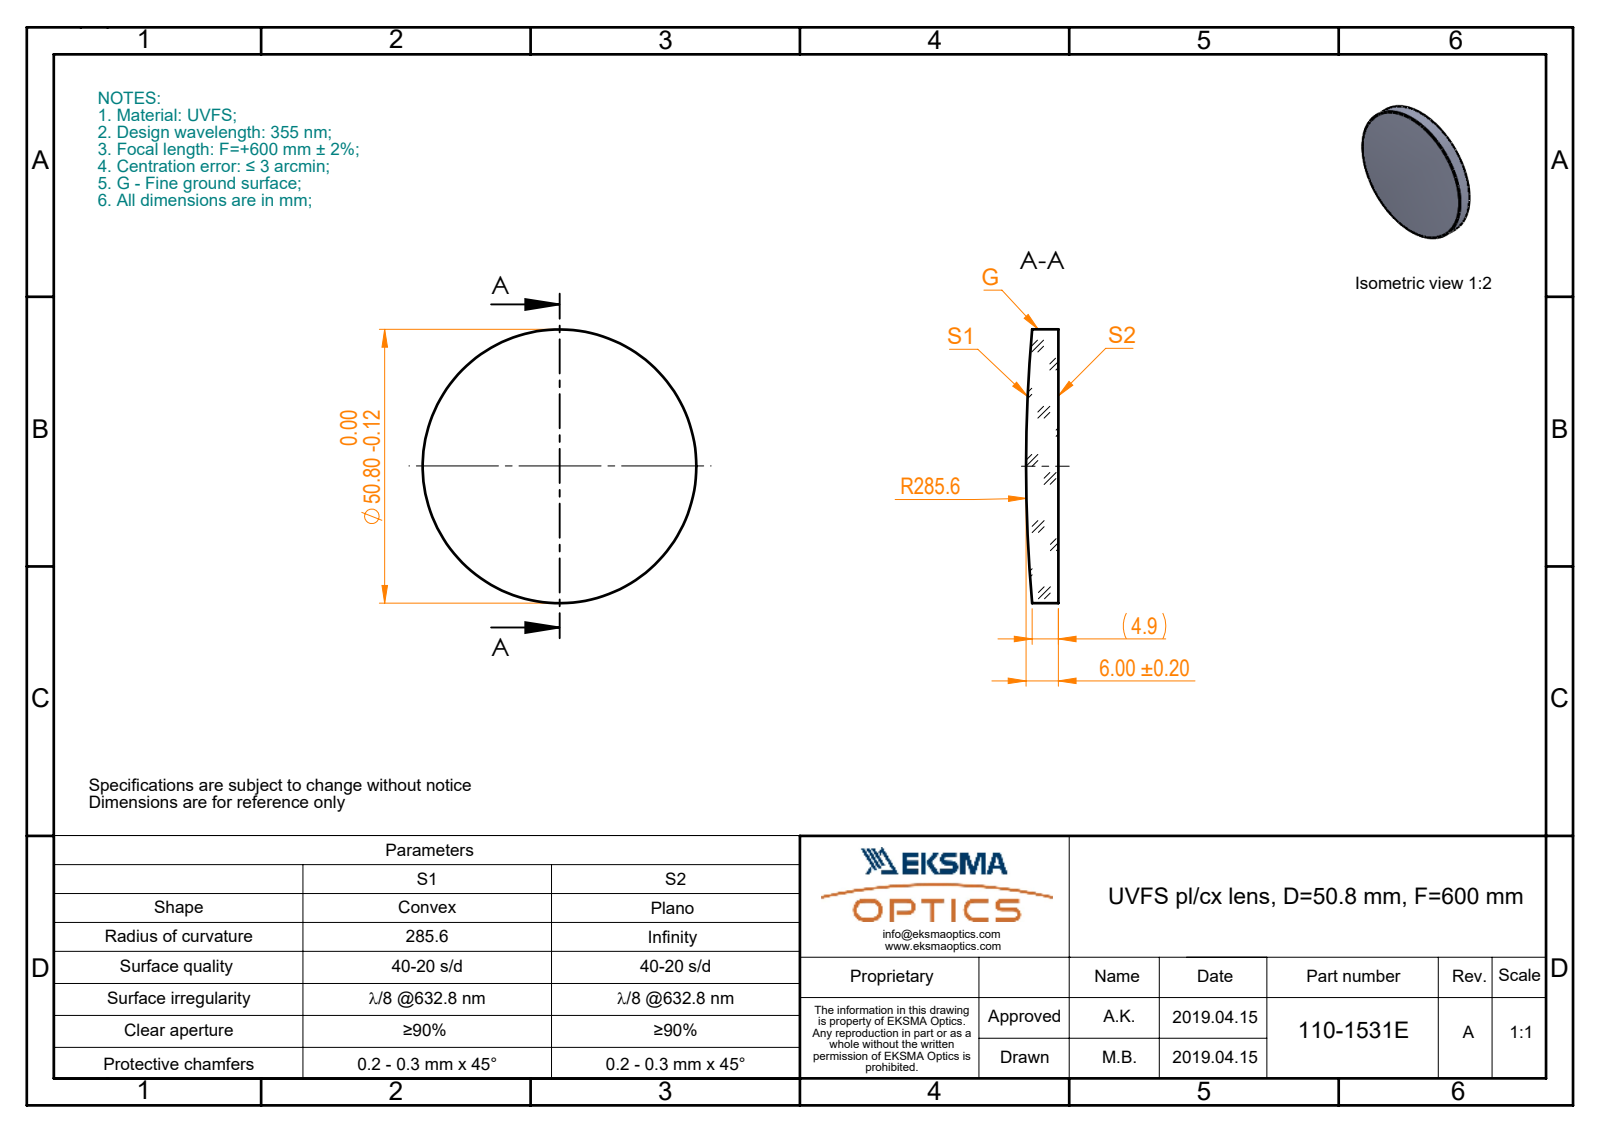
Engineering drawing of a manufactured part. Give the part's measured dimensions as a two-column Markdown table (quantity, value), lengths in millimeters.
| quantity | value |
| --- | --- |
| part name | 110-1531E UVFS pl-cx 50.8 F600 |
| STEP written by | SolidWorks 2017 (CONFIG_CONTROL_DESIGN) |
| units | millimeters |
| bodies | 1 solid, 5 faces (1 planar, 2 cylindrical, 2 other) |
| overall size | 50.8 × 50.8 × 6 |
| volume | 11 015 mm³ |
| surface area | 4 835 mm² |
| round bosses / shafts (diameter × count) | 50.8 × 1 |
